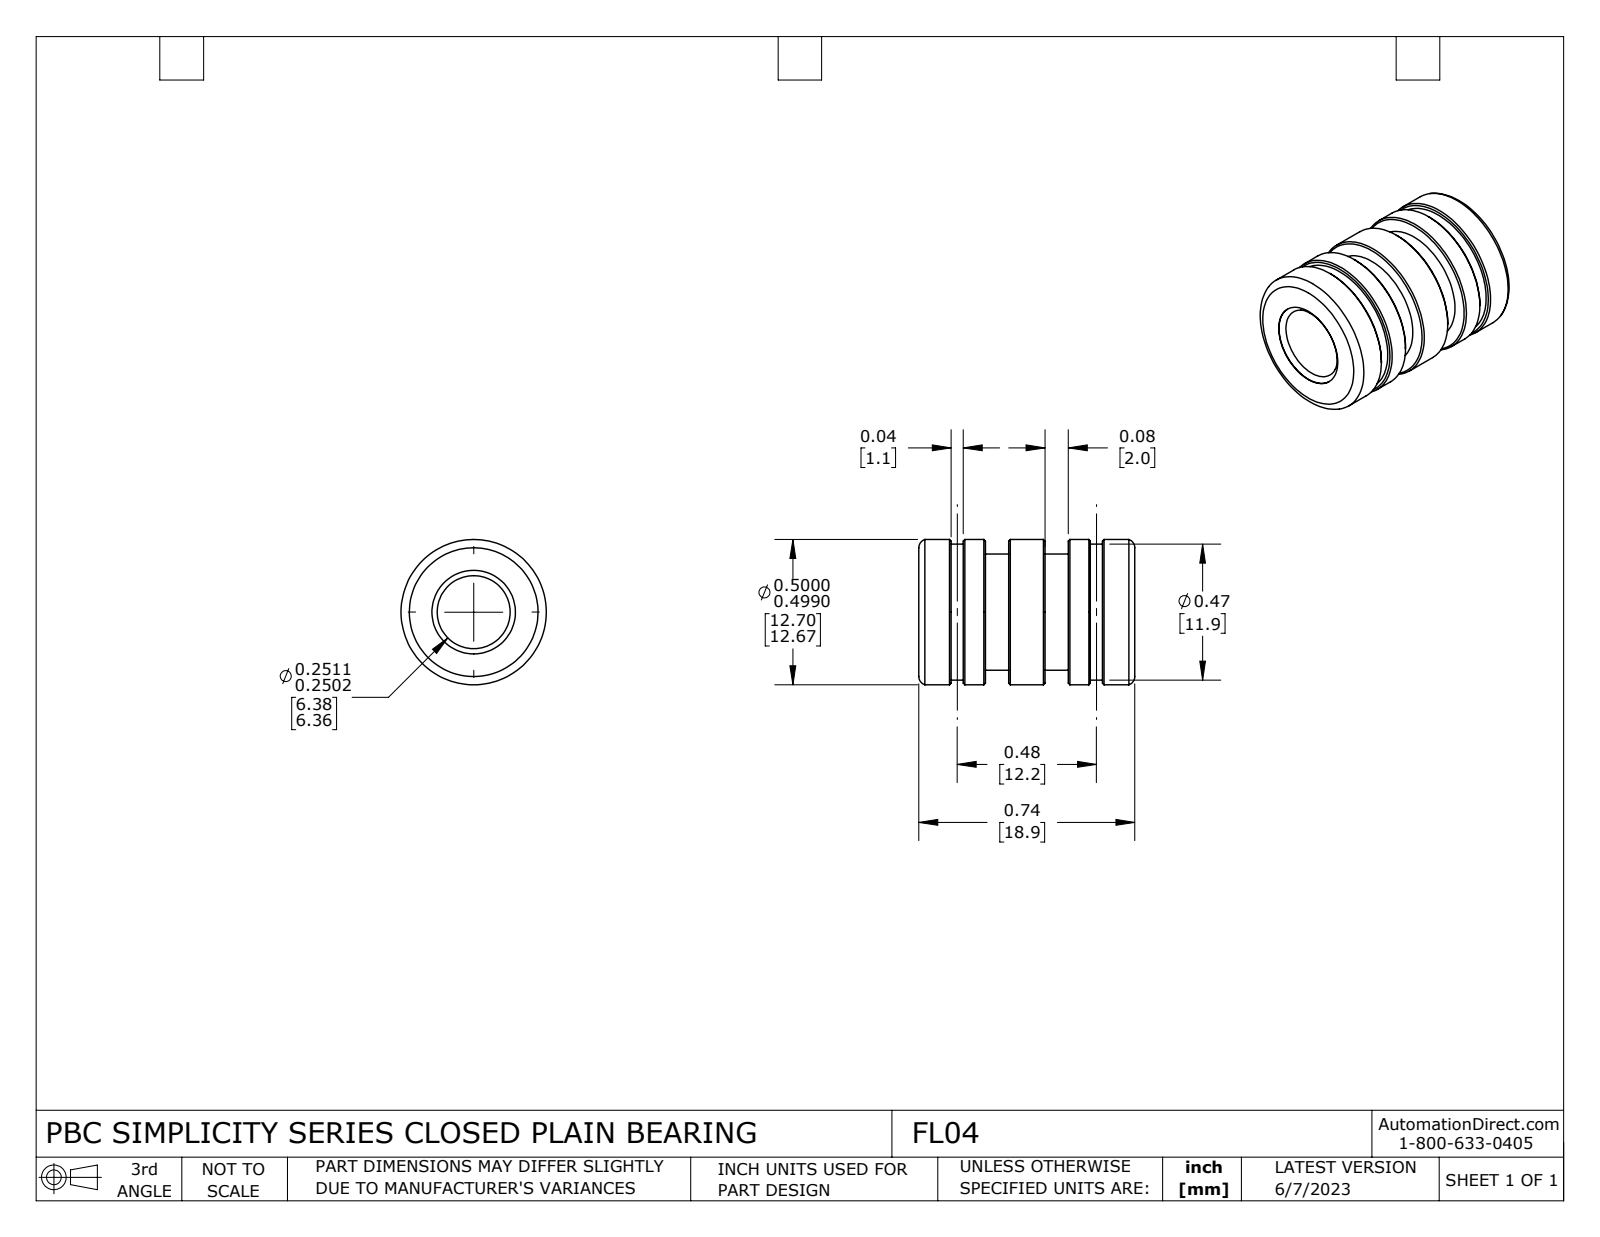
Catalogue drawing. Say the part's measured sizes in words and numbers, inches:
The part is named "FL04". Its 3-D file was written by "SolidWorks 2021 (CONFIG_CONTROL_DESIGN)". It is 2 solids with 58 faces: 10 planar, 24 cylindrical and 24 other. Overall it measures 0.743 by 0.499 by 0.499 inches. Its volume is 0.094 cubic inches and its surface area 3.607 square inches. Round holes: 1 of diameter 0.251, 1 of diameter 0.287. Round bosses or shafts: 1 of diameter 0.499, 1 of diameter 0.467, 1 of diameter 0.399. The main face-to-face distances are 0.229, 0.309, 0.434, 0.514, 0.08, 0.205, 0.743, 0.285, 0.125, 0.153.
